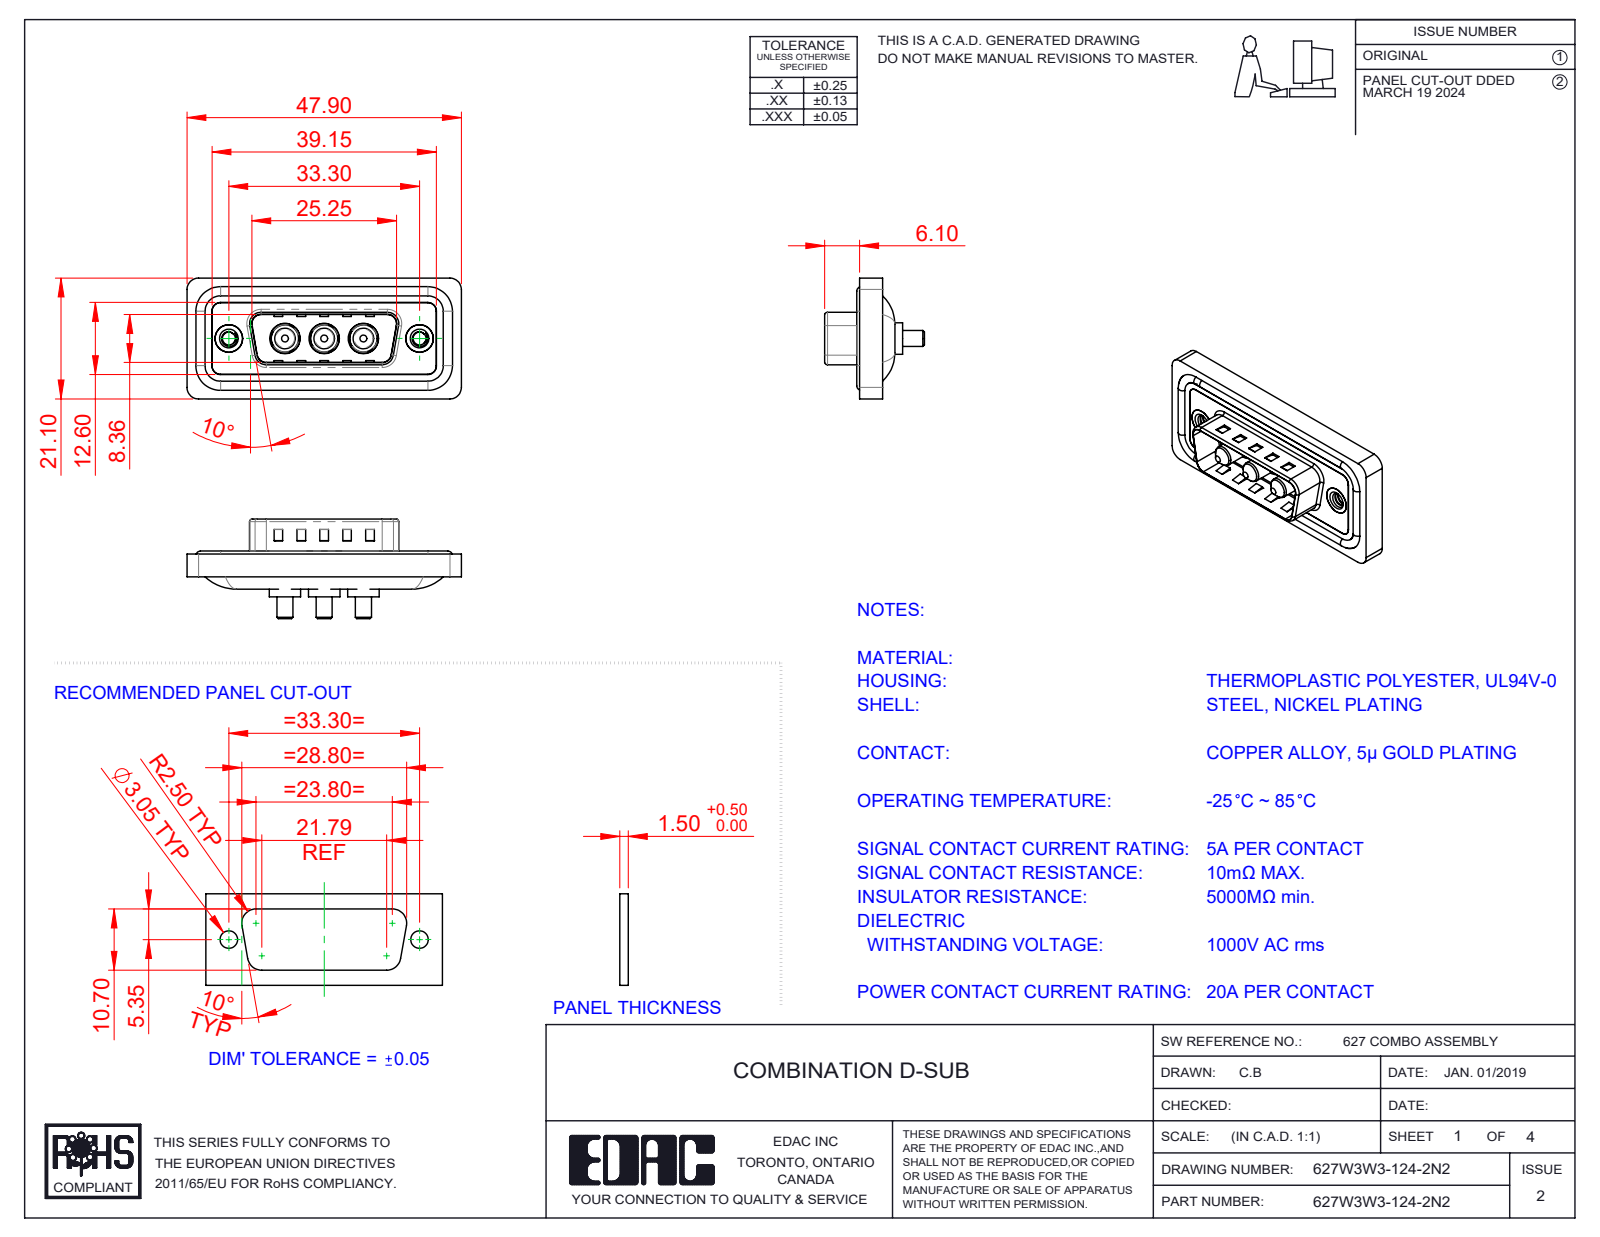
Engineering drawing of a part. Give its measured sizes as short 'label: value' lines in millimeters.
name: 627Combo Shell Rear_15 Contacts; 627Combo Housing_3W3; 627Combo Threaded Rivet_2; 627W3W3-124-2N2 (+3 more)
written by: SolidWorks 2023 (CONFIG_CONTROL_DESIGN)
unit: mm
bodies: 13 solids, 564 faces (207 planar, 241 cylindrical, 116 other)
size: 47.9 × 21.1 × 17.4
volume: 5 586 mm³; area: 8 753 mm²
holes: 3× ⌀4.85, 3× ⌀5.3, 2× ⌀2.26, 2× ⌀4, 2× ⌀4.8, 2× ⌀5
bosses: 4× ⌀1.6, 3× ⌀5.5, 3× ⌀5.2, 3× ⌀4.75, 3× ⌀3.75, 3× ⌀3.6, 3× ⌀2.8, 2× ⌀4.9
rounds: 26× R1.5, 20× R2, 8× R0.5, 8× R1.6, 4× R0.25, 4× R0.6, 4× R0.65, 4× R0.9
face distances: 0.4, 1.1, 1.5, 0.5, 1.6, 3.1, 2.9, 4, 0.82, 9.58
hole spacings: 6.85, 9.8, 16.65, 23.5, 13.7, 33.3
